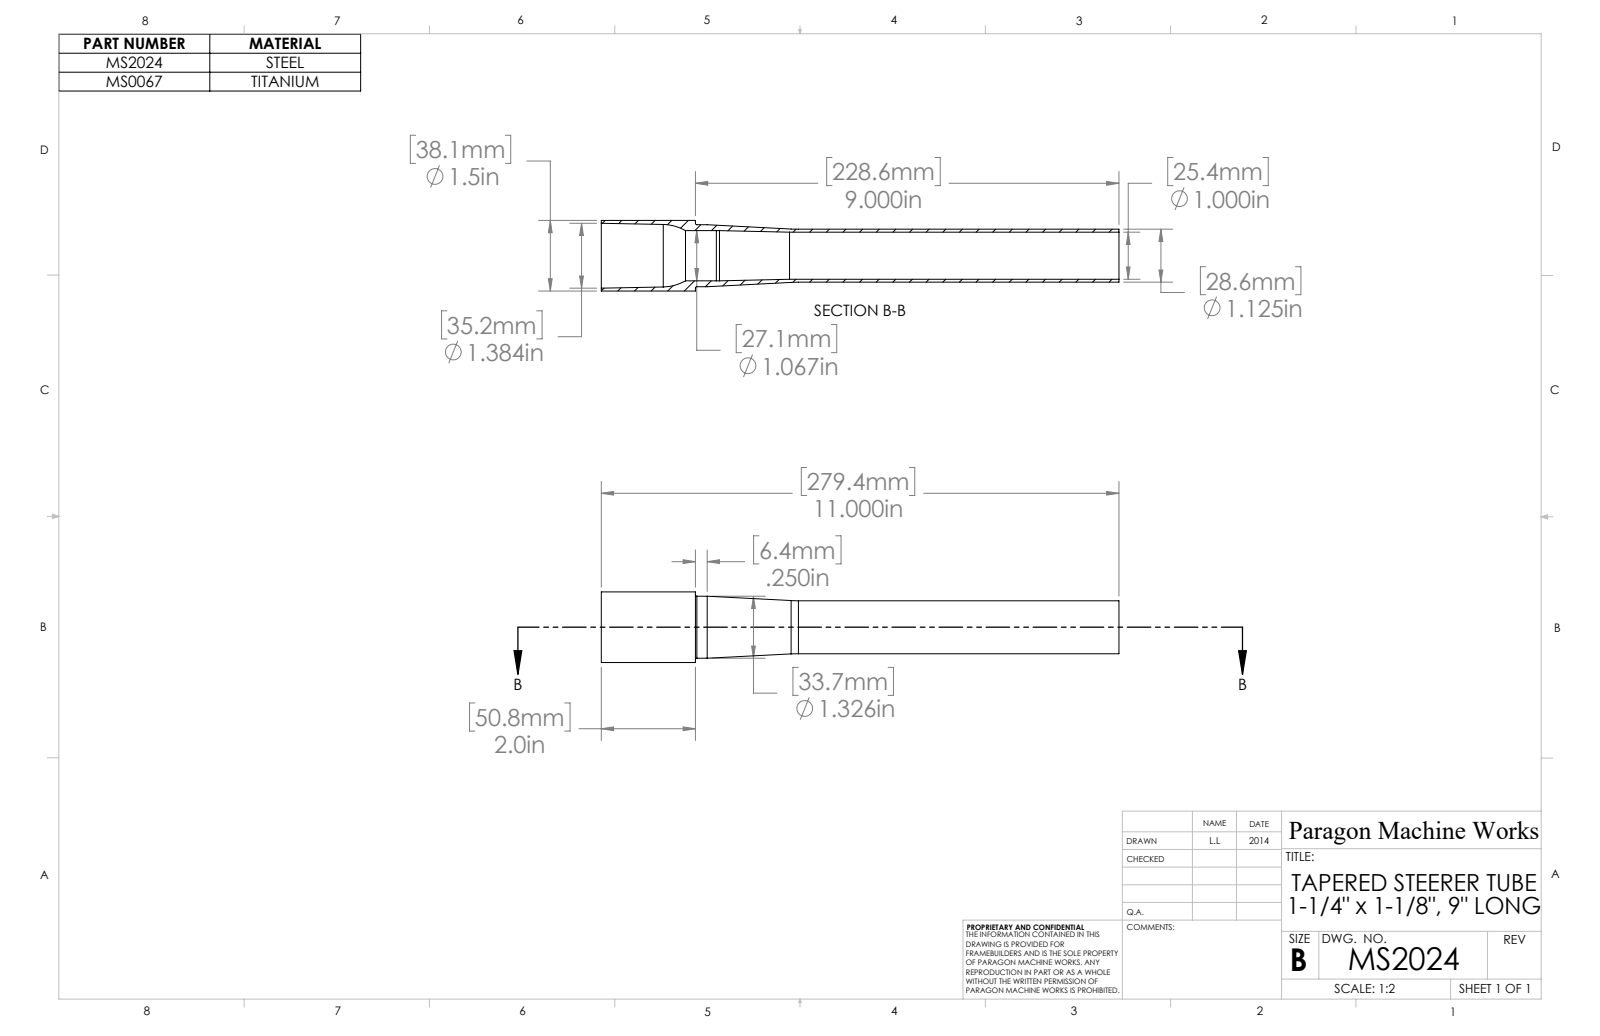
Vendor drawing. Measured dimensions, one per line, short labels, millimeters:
name: MS2024
written by: SolidWorks 2012 (CONFIG_CONTROL_DESIGN)
unit: mm
bodies: 1 solid, 15 faces (3 planar, 5 cylindrical, 7 other)
size: 279.4 × 38.1 × 38.1
volume: 50 010 mm³; area: 51 320 mm²
holes: 1× ⌀25.4, 1× ⌀27.1
bosses: 1× ⌀38.1, 1× ⌀33.5, 1× ⌀28.6
face distances: 50.8, 279.4, 228.6
